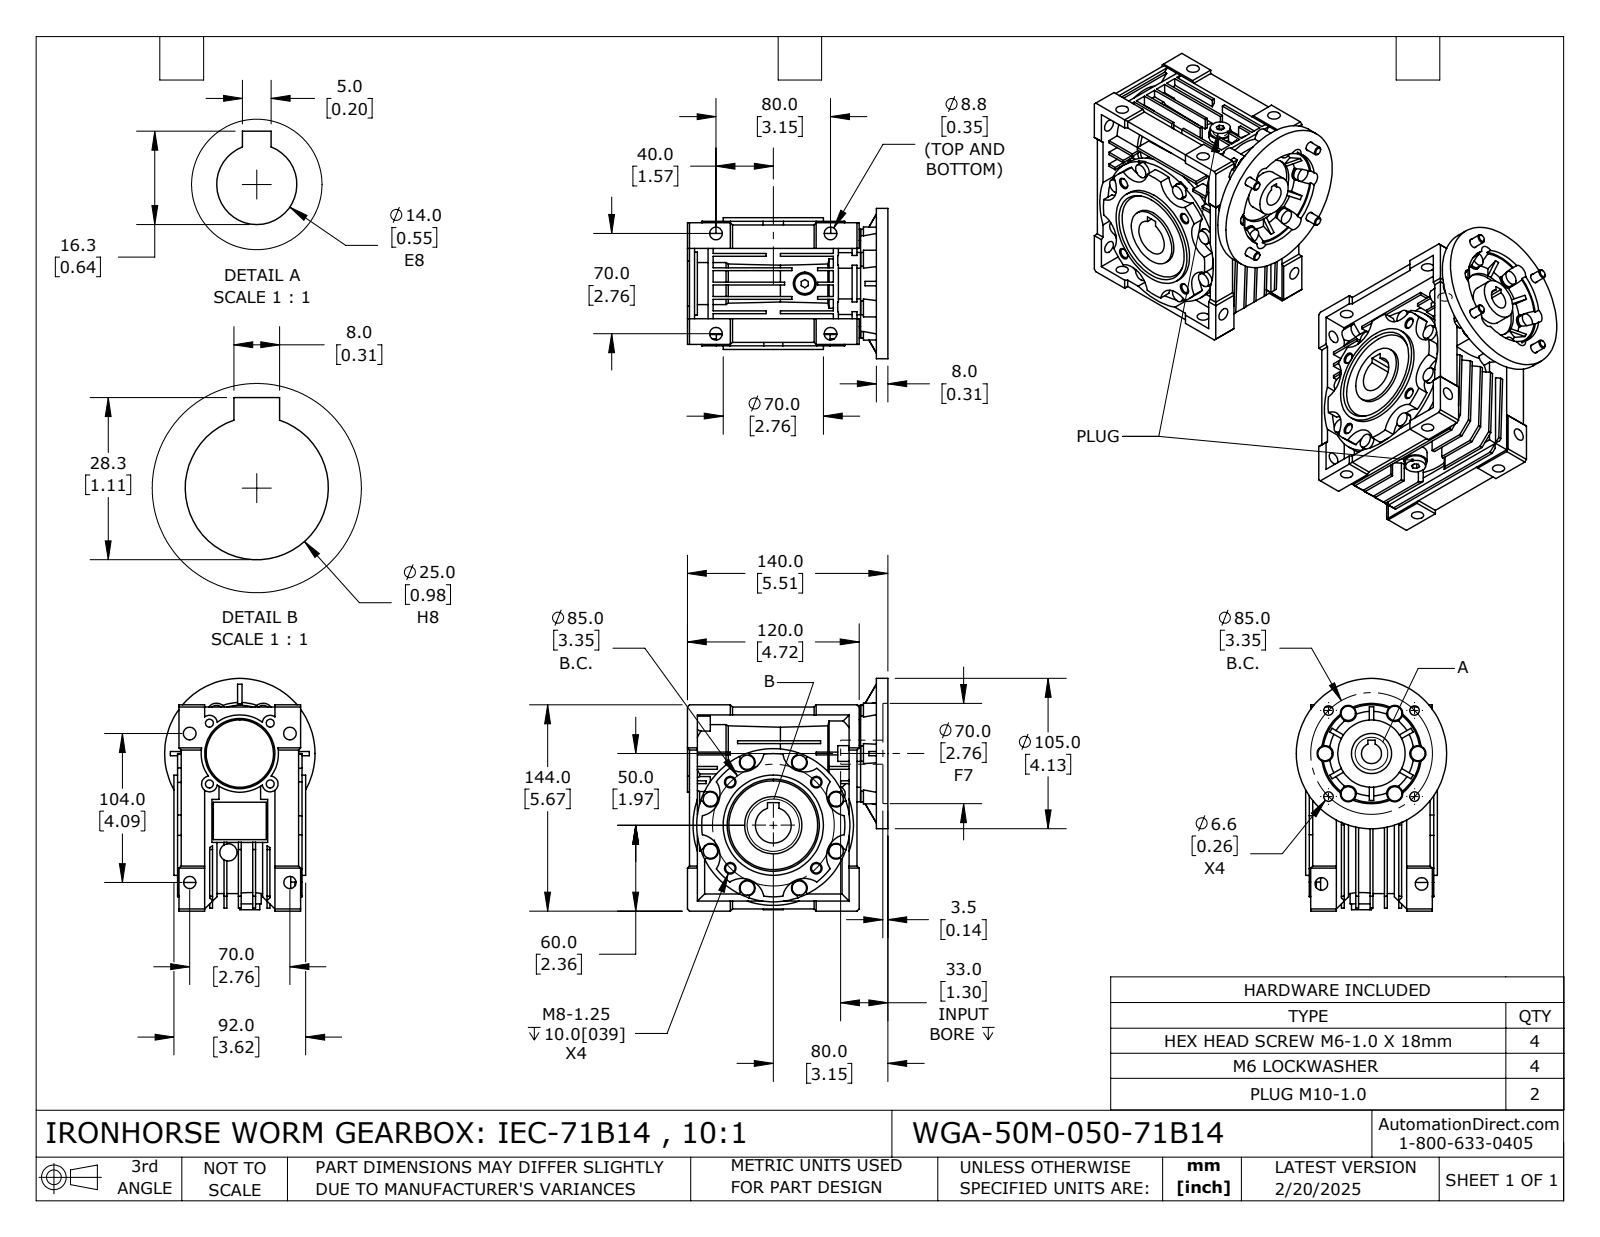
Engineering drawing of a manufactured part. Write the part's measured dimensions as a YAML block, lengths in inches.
part_name: "WGA-50M-050-71B14"
step_written_by: "SolidWorks 2024 (CONFIG_CONTROL_DESIGN)"
units: inches
bodies: {solids: 15, faces: 1132, planar: 615, cylindrical: 372, other: 145}
overall_size: [6.398, 5.846, 4.134]
volume: 64.99
surface_area: 364.6
round_holes:
  - {diameter: 0.346, count: 8}
  - {diameter: 0.335, count: 6}
  - {diameter: 0.219, count: 4}
  - {diameter: 0.24, count: 4}
  - {diameter: 0.26, count: 4}
  - {diameter: 0.262, count: 2}
  - {diameter: 0.262, count: 2}
  - {diameter: 0.354, count: 2}
  - {diameter: 0.551, count: 1}
  - {diameter: 0.591, count: 1}
  - {diameter: 0.984, count: 1}
  - {diameter: 1.102, count: 1}
round_bosses_or_shafts:
  - {diameter: 0.394, count: 14}
  - {diameter: 0.48, count: 4}
  - {diameter: 0.236, count: 4}
  - {diameter: 0.63, count: 2}
  - {diameter: 0.551, count: 2}
  - {diameter: 0.386, count: 2}
  - {diameter: 0.327, count: 2}
  - {diameter: 4.213, count: 1}
partial_cylinders:
  - {radius: 0.217, count: 18}
  - {radius: 0.236, count: 8}
  - {radius: 0.591, count: 8}
  - {radius: 0.61, count: 8}
  - {radius: 0.226, count: 6}
  - {radius: 0.276, count: 6}
  - {radius: 0.817, count: 1}
  - {radius: 1.378, count: 1}
face_to_face_distances: [0.315, 0.079, 0.394, 0.276, 0.059, 0.217, 0.787, 0.472, 2.165, 1.378]
hole_center_spacings: [1.673, 2.048, 2.366, 2.756, 0.492, 1.181, 1.67, 2.854]
